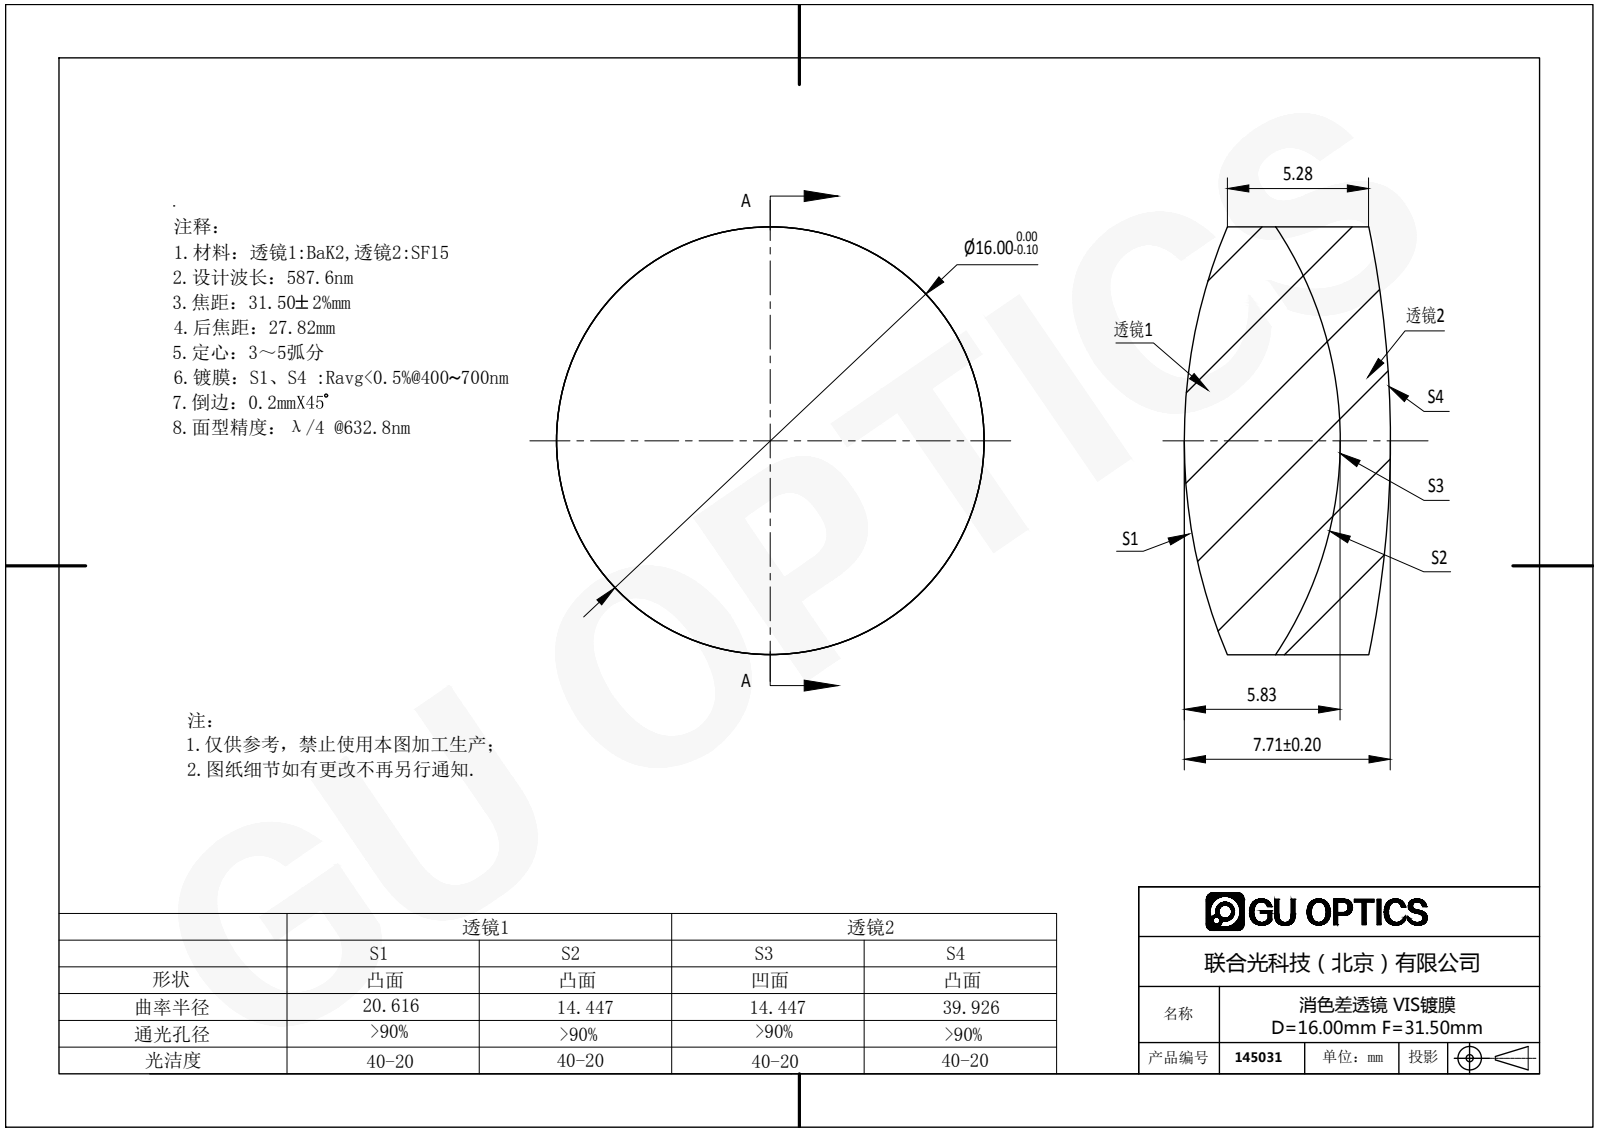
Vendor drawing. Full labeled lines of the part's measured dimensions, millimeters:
Part name (STEP PRODUCT): 145031
STEP written by: SolidWorks 2016 (AUTOMOTIVE_DESIGN)
Units: millimetres
Bodies: 2 solids, 12 faces (0 planar, 4 cylindrical, 8 other)
Overall size (bounding box): 16 × 16 × 7.71
Volume: 1 309 mm³ · Surface area: 1 117 mm²
Round bosses / shafts (diameter × count): ⌀16 ×1
